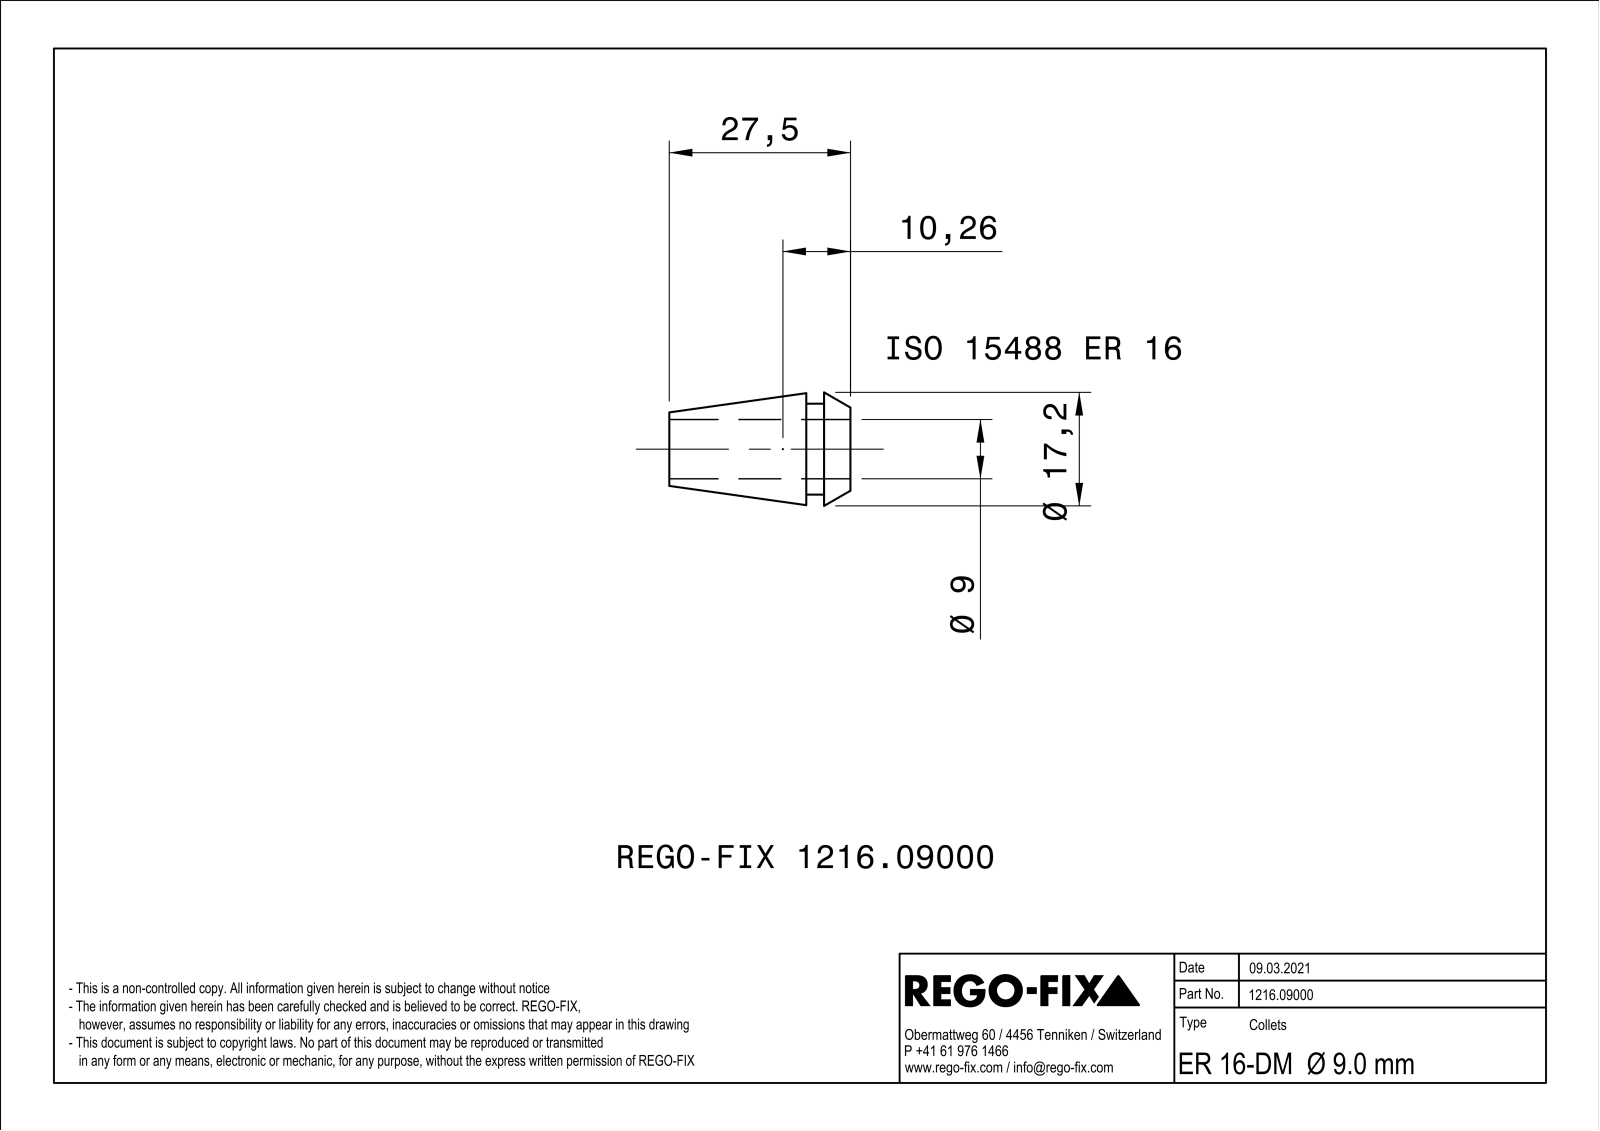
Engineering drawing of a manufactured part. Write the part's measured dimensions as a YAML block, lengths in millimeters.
part_name: "NOCUT"
step_written_by: "SIEMENS PLM Software Solid Edge ST10 (AUTOMOTIVE_DESIGN)"
units: millimeters
bodies: {solids: 1, faces: 154, planar: 80, cylindrical: 9, other: 65}
overall_size: [27.5, 16.99, 16.99]
volume: 2187
surface_area: 3414
round_holes:
  - {diameter: 9, count: 1}
round_bosses_or_shafts:
  - {diameter: 13.8, count: 1}
face_to_face_distances: [0.6, 2.7, 4, 6.7, 27.5, 23.5, 20.8, 13, 9, 6.3]
